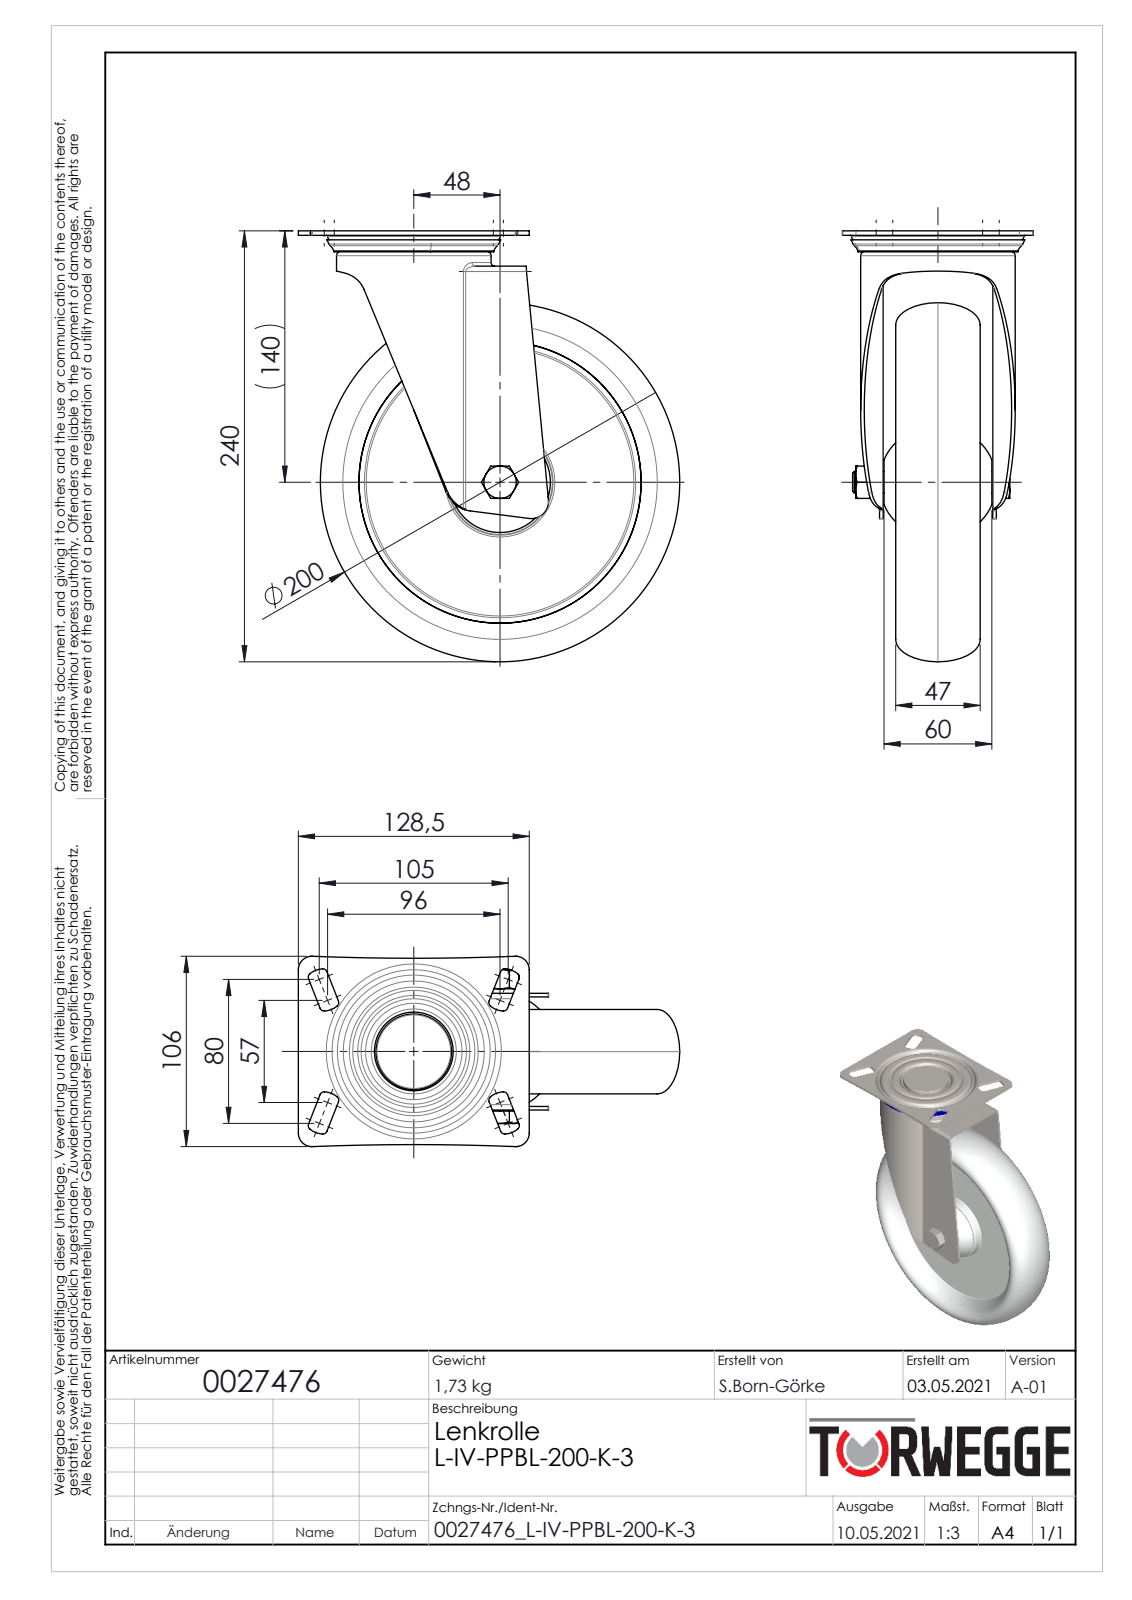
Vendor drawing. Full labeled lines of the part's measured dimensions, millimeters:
Part name (STEP PRODUCT): 0027476
STEP written by: SolidWorks 2020 (AUTOMOTIVE_DESIGN)
Units: millimetres
Bodies: 11 solids, 435 faces (93 planar, 103 cylindrical, 239 other)
Overall size (bounding box): 240 × 212.25 × 106
Volume: 886 040 mm³ · Surface area: 292 041 mm²
Round holes (diameter × count): ⌀10.2 ×1, ⌀12 ×1, ⌀12.2 ×1, ⌀12.3 ×1, ⌀34 ×1, ⌀38 ×1, ⌀44 ×1, ⌀47 ×1, ⌀50.5 ×1, ⌀54 ×1, ⌀82 ×1
Round bosses / shafts (diameter × count): ⌀89 ×1, ⌀86 ×1, ⌀54.5 ×1, ⌀42 ×1, ⌀41 ×1, ⌀38 ×1, ⌀20.2 ×1, ⌀20 ×1
Partial cylindrical surfaces — rounded edges, fillets, slot ends (radius × count): R2.5 ×16, R1 ×4, R7.5 ×4, R11.75 ×4, R2 ×2, R3 ×2, R1424.42 ×2, R9.5 ×1
Main face-to-face distances: 11, 2, 27, 38, 25, 36, 63, 2.5, 65, 61
